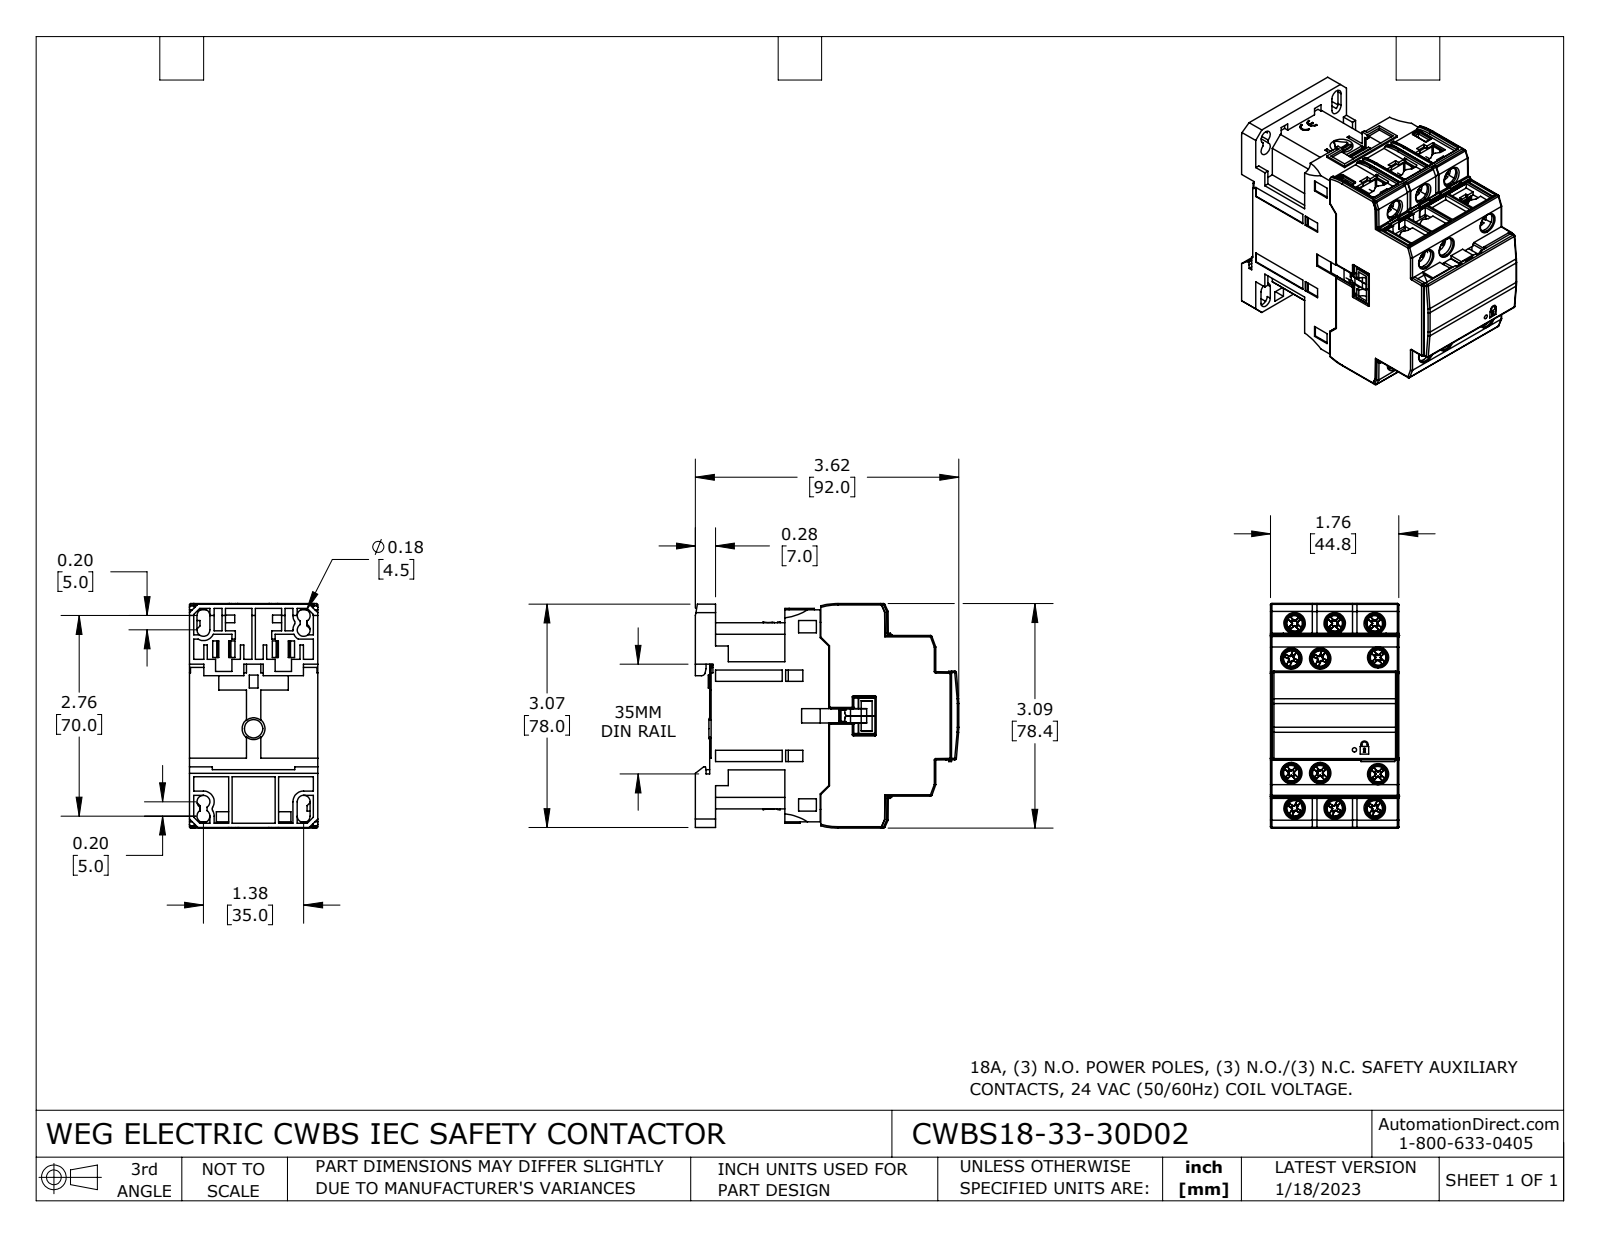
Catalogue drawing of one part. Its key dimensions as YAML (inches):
part_name: "CWBS18-33-30D02"
step_written_by: "SolidWorks 2021 (CONFIG_CONTROL_DESIGN)"
units: inches
bodies: {solids: 45, faces: 3295, planar: 2311, cylindrical: 624, other: 360}
overall_size: [3.62, 3.087, 1.764]
volume: 13.51
surface_area: 120.4
round_holes:
  - {diameter: 0.124, count: 12}
  - {diameter: 0.256, count: 6}
  - {diameter: 0.177, count: 4}
  - {diameter: 0.059, count: 1}
round_bosses_or_shafts:
  - {diameter: 0.169, count: 12}
  - {diameter: 0.138, count: 12}
  - {diameter: 0.107, count: 8}
  - {diameter: 0.107, count: 4}
partial_cylinders:
  - {radius: 0.02, count: 139}
  - {radius: 0.012, count: 52}
  - {radius: 0.071, count: 24}
  - {radius: 0.964, count: 24}
  - {radius: 2.128, count: 24}
  - {radius: 0.016, count: 20}
  - {radius: 0.039, count: 19}
  - {radius: 0.106, count: 11}
face_to_face_distances: [1.764, 0.047, 1.717, 3.305, 1.754, 1.551, 0.276, 0.022, 1.776, 1.53]
hole_center_spacings: [0.551, 1.102, 0.197, 0.398, 0.795, 1.193, 1.341, 1.575]
